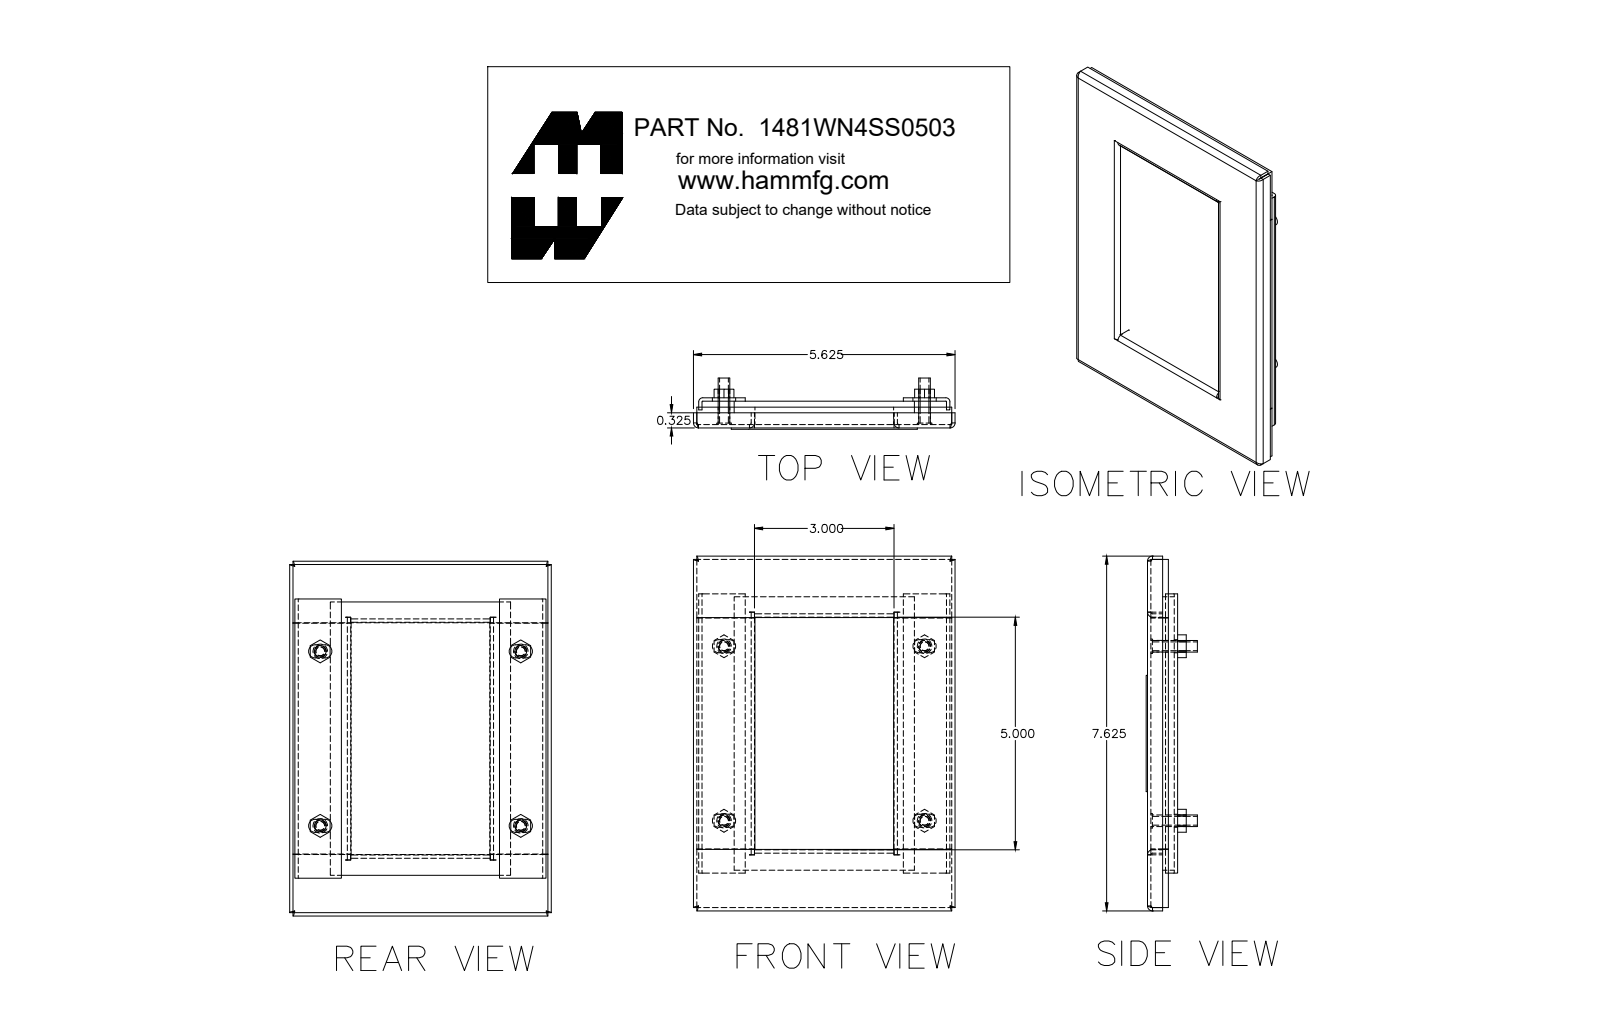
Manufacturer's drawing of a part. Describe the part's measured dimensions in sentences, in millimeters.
The part is named "1481WN4SS0503_Default". Its 3-D file was written by "SolidWorks 2019 (CONFIG_CONTROL_DESIGN)". It is 13 solids with 202 faces: 142 planar, 52 cylindrical and 8 other. Overall it measures 203.8 by 153 by 27.2 millimeters. Its volume is 200 700 cubic millimeters and its surface area 154 600 square millimeters. Round holes: 4 of diameter 5, 4 of diameter 8.3. Round bosses or shafts: 4 of diameter 8, 4 of diameter 6.4. Partial cylindrical surfaces (rounded edges, fillets, slot ends): 8 of radius 0.9, 8 of radius 2.7, 2 of radius 0.4, 2 of radius 2.2. The main face-to-face distances are 1.8, 14.6, 12.8, 8.3, 6.4, 6.4, 14.6, 16.4, 8.2, 1.8. The hole center spacings are 109.6, 95.3, 145.2, 145.2, 145.2, 95.2, 95.3, 95.3.
